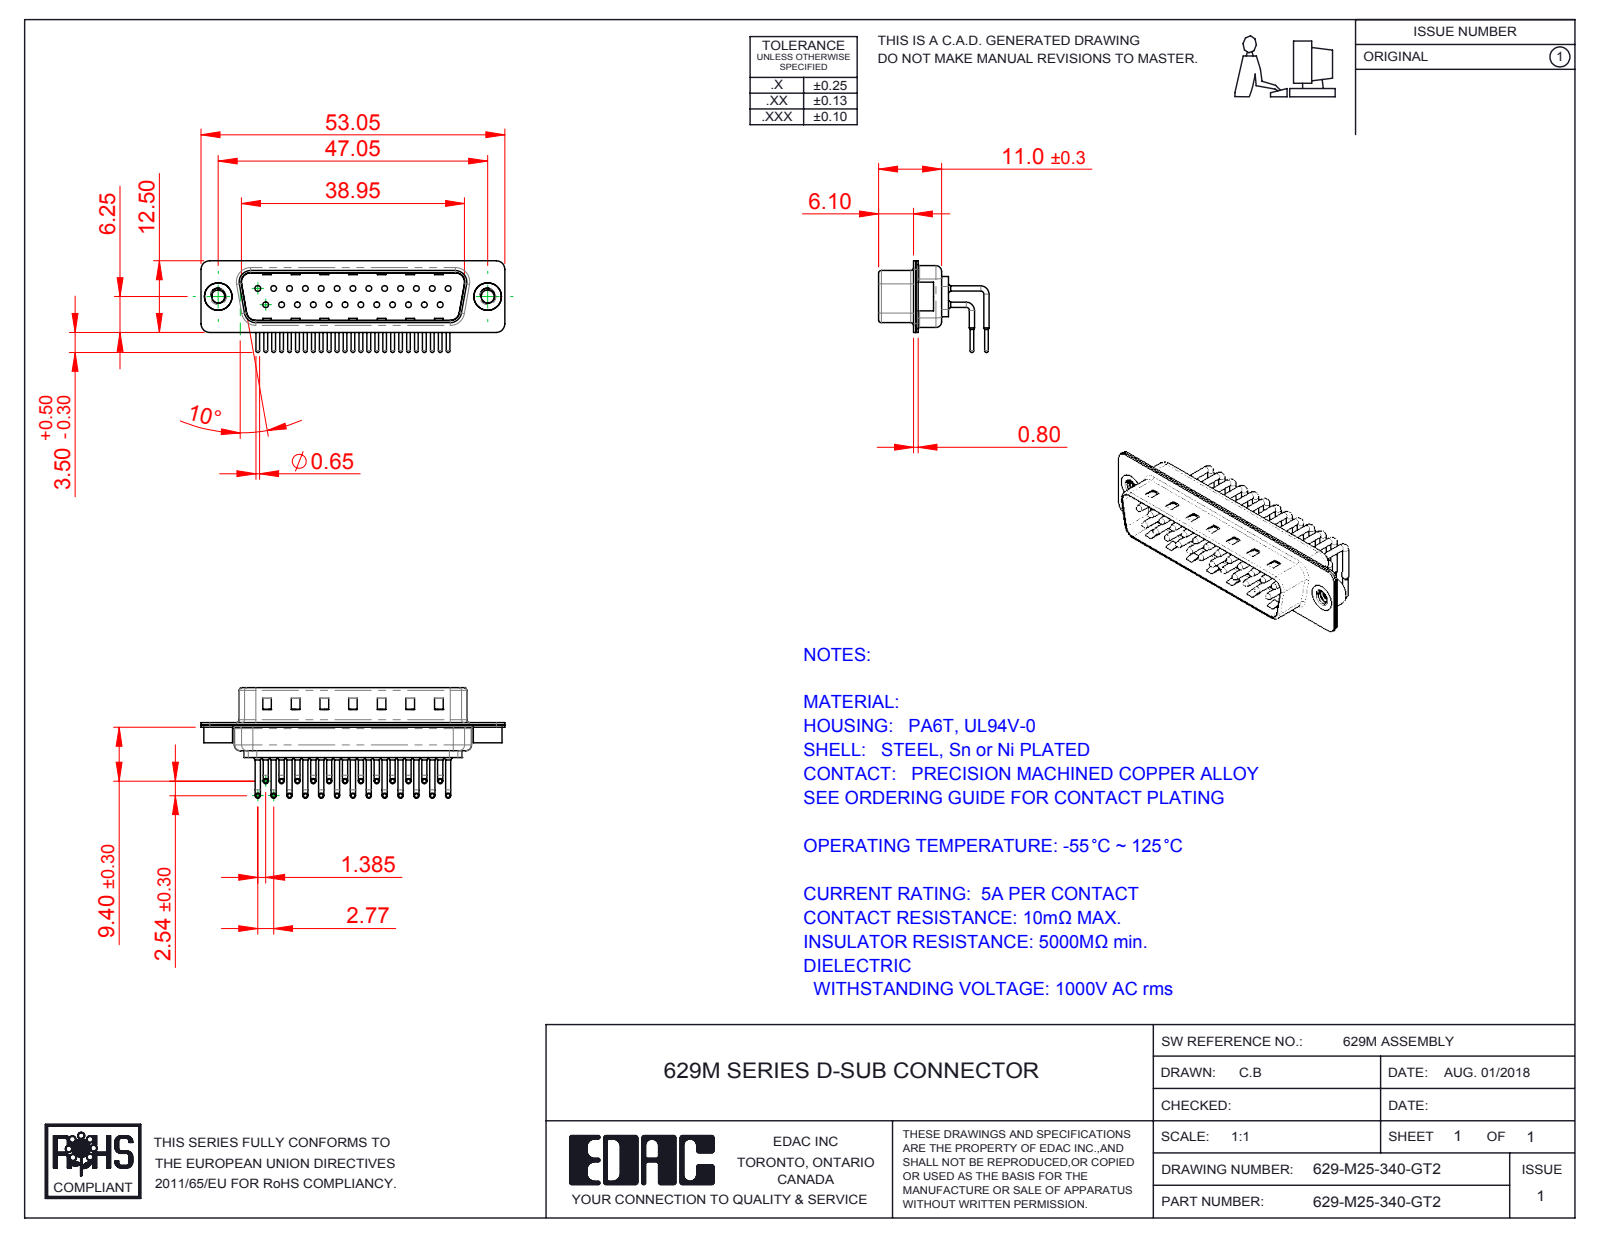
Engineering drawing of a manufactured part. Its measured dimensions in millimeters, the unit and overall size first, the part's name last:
Units: millimetres
Overall size (bounding box): 53.05 × 19.29 × 16
Round holes (diameter × count): ⌀1 ×25, ⌀1.7 ×25, ⌀2 ×25, ⌀2.26 ×2, ⌀4 ×2, ⌀4.8 ×2
Round bosses / shafts (diameter × count): ⌀0.9 ×50, ⌀1.5 ×25, ⌀0.65 ×25, ⌀5 ×2, ⌀4.9 ×2
Partial cylindrical surfaces — rounded edges, fillets, slot ends (radius × count): R1.01 ×25, R1.5 ×16, R2 ×12, R0.5 ×8, R1.6 ×8, R0.25 ×4, R0.6 ×4, R0.65 ×4
Main face-to-face distances: 0.4, 0.85, 9.55, 8.7, 1.25, 10.4, 1.5, 1.9, 0.35, 6.1
Hole centre spacings: 3.16, 2.77, 5.54, 8.31, 11.08, 13.85, 5.04, 7.49
Volume: 2 911 mm³ · Surface area: 7 760 mm²
Bodies: 30 solids, 3126 faces (1771 planar, 1037 cylindrical, 318 other)
Part name (STEP PRODUCT): 629M 4-40 Threaded Rivet; 629M Shell Front_25 Contacts; 629M Housing_25 Contacts; 629-M25-340-GT2 (+3 more)
STEP written by: SolidWorks 2016 (CONFIG_CONTROL_DESIGN)
